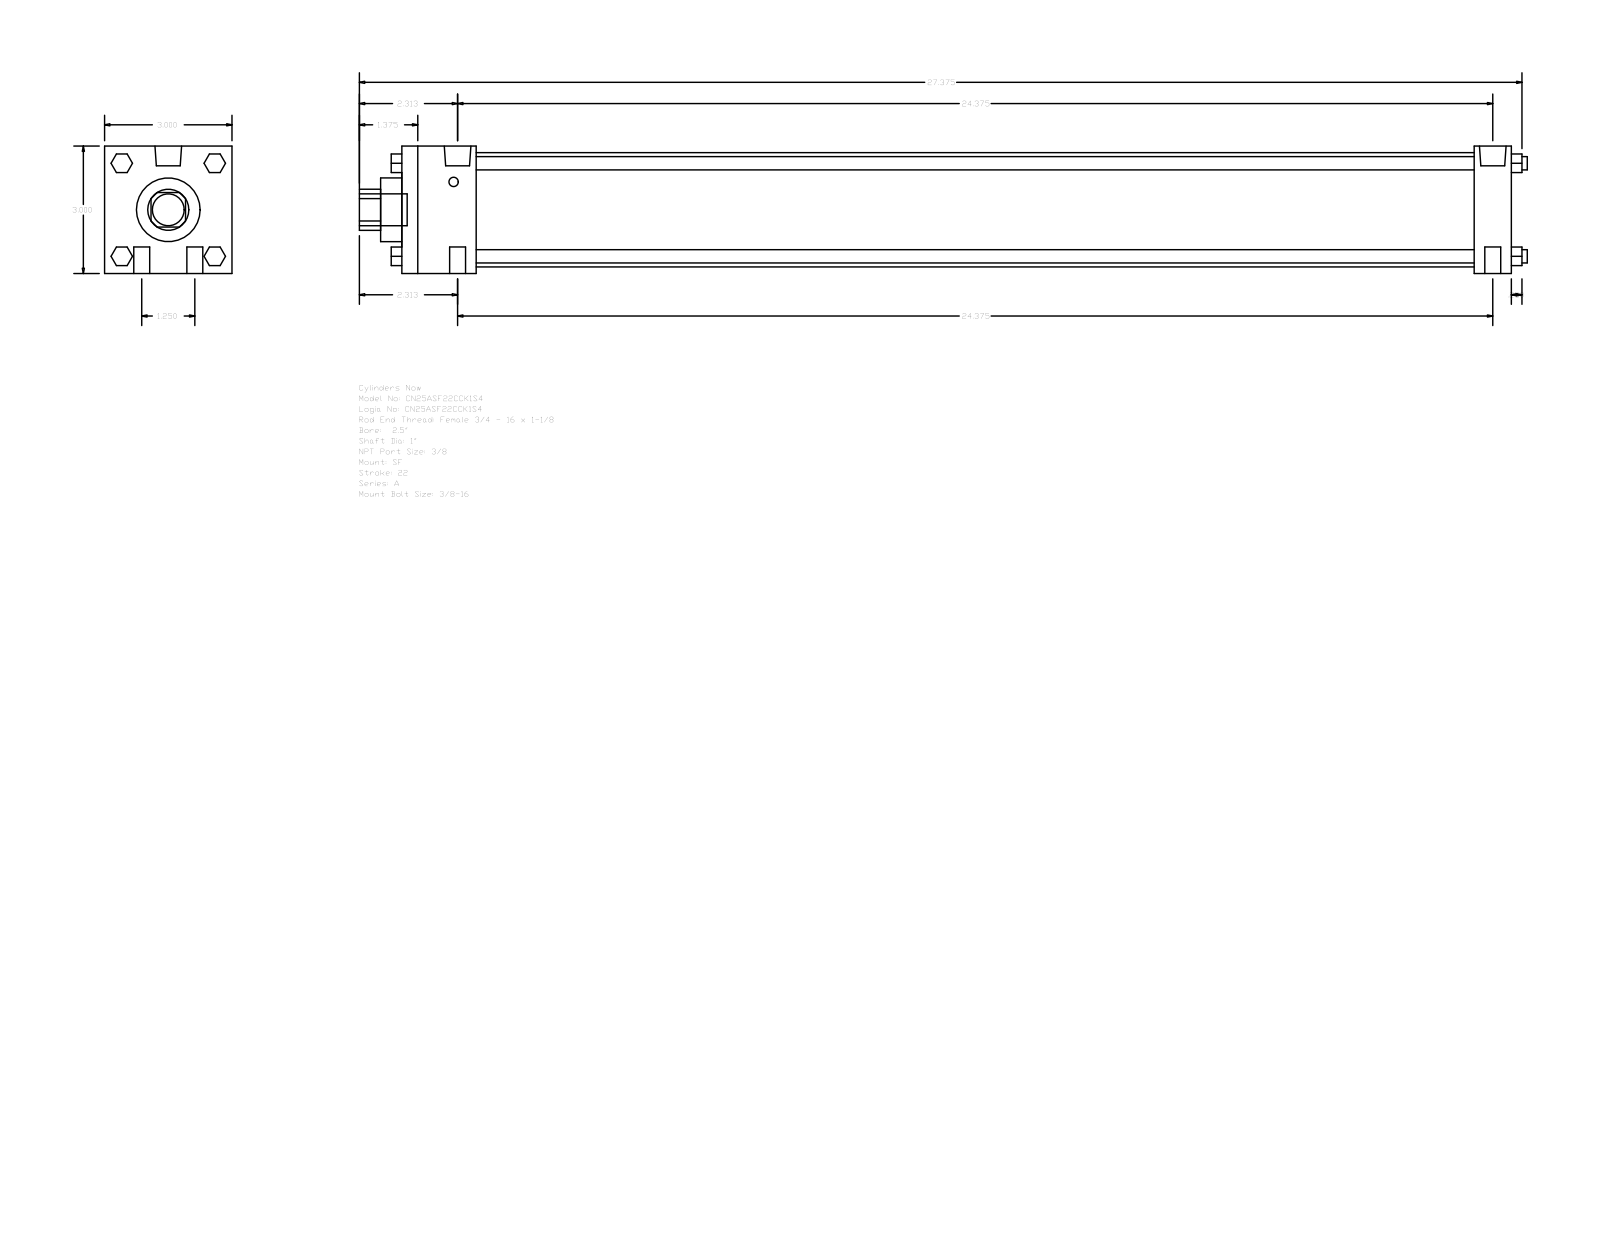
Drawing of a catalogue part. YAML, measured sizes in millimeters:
part_name: "A_SF__0250_1"
step_written_by: "GSSL Pune (CONFIG_CONTROL_DESIGN)"
units: millimeters
bodies: {solids: 0, faces: 124, planar: 94, cylindrical: 30, other: 0}
overall_size: [698.5, 76.2, 76.2]
round_holes:
  - {diameter: 25.4, count: 1}
  - {diameter: 38.1, count: 1}
  - {diameter: 68.33, count: 1}
round_bosses_or_shafts:
  - {diameter: 9.53, count: 4}
  - {diameter: 7.94, count: 4}
  - {diameter: 15.93, count: 2}
  - {diameter: 5.56, count: 2}
  - {diameter: 19.05, count: 1}
partial_cylinders:
  - {radius: 12.29, count: 1}
face_to_face_distances: [76.2, 663.58, 641.35, 22.23, 44.45, 596.9, 619.13, 12.7, 676.28, 6.35]
